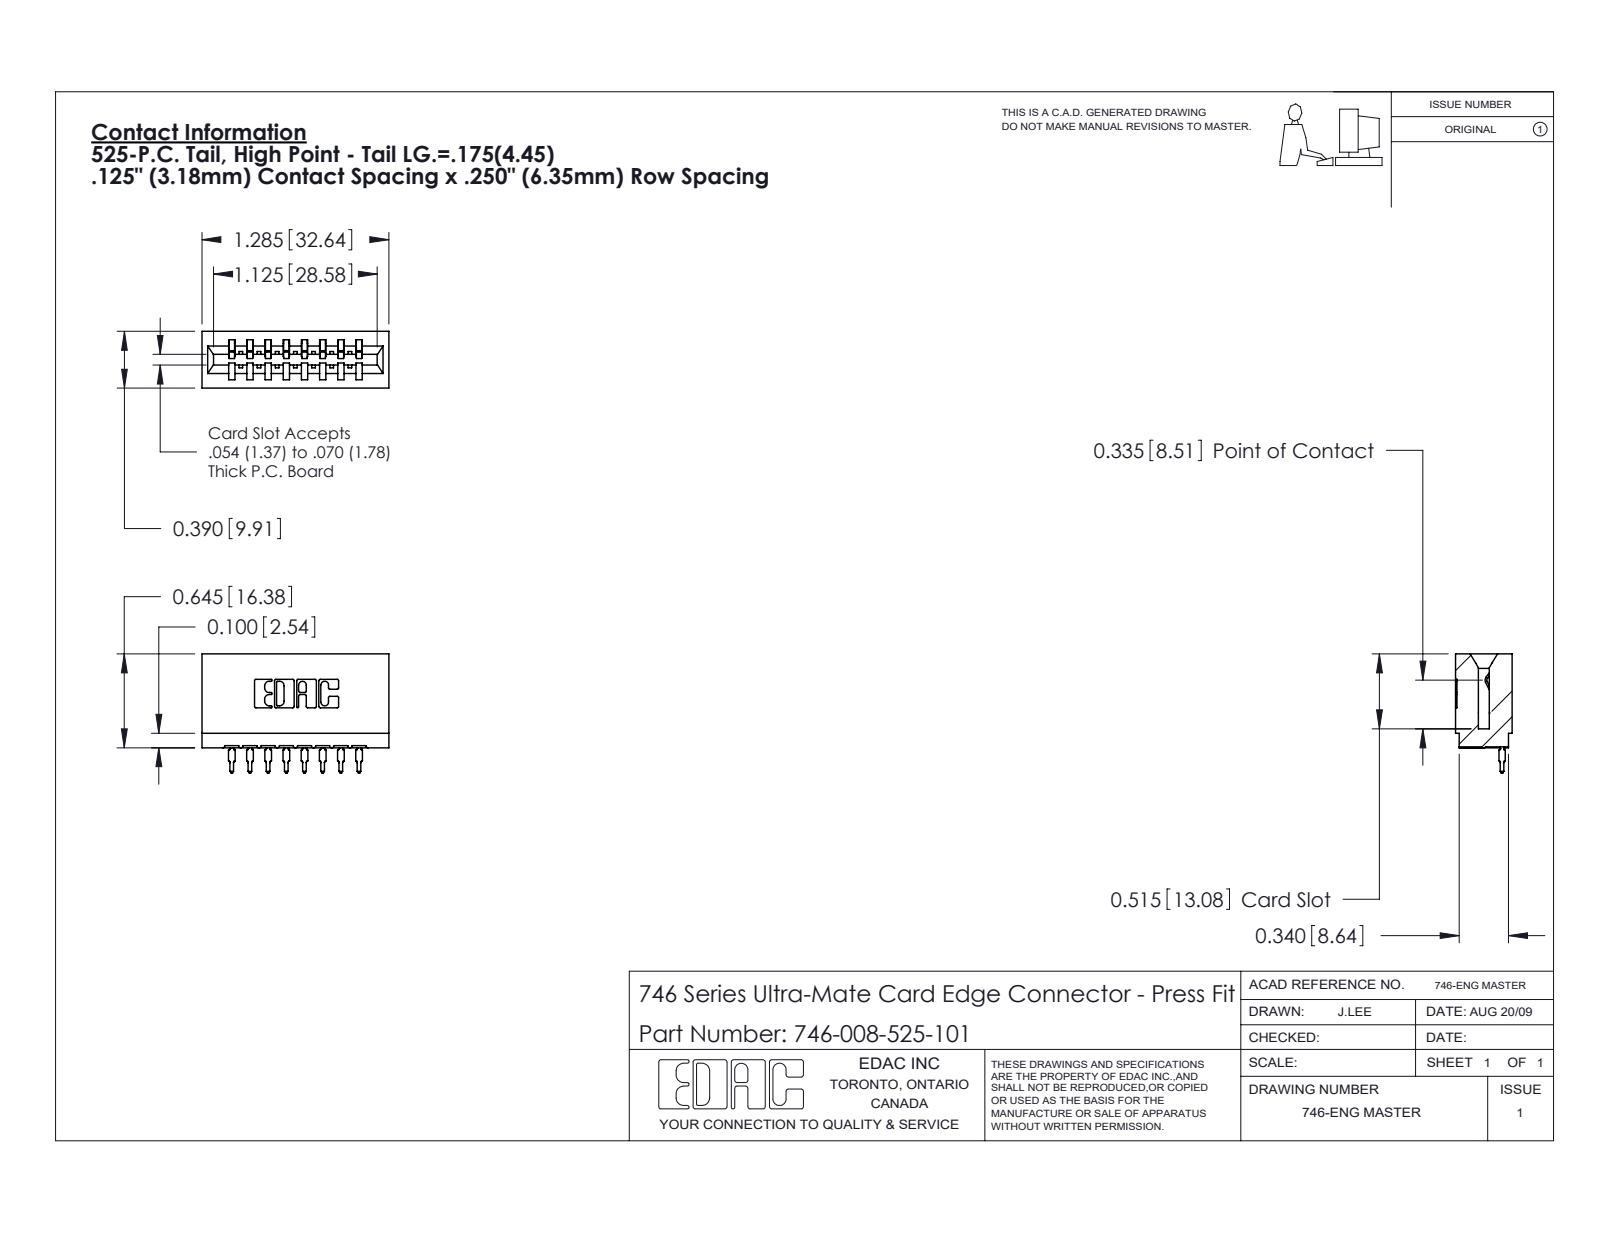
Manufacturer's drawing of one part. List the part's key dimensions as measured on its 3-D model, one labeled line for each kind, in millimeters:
Part name (STEP PRODUCT): 746-292-001_525; 746 Part_.515 Slot Depth - 01; 746-008-525-101
STEP written by: SolidWorks 2020 (CONFIG_CONTROL_DESIGN)
Units: millimetres
Bodies: 9 solids, 961 faces (559 planar, 194 cylindrical, 208 other)
Overall size (bounding box): 32.6 × 20.8 × 9.9
Volume: 3 640 mm³ · Surface area: 4 774 mm²
Partial cylindrical surfaces — rounded edges, fillets, slot ends (radius × count): R0.3 ×22, R0.5 ×16, R0.4 ×9, R0.2 ×6, R0.8 ×6, R0.1 ×4, R0.3 ×4, R0.7 ×3
Main face-to-face distances: 6.4, 1.1, 3.2, 12.7, 8.5, 7.4, 5.3, 9.5, 3.2, 1.4
